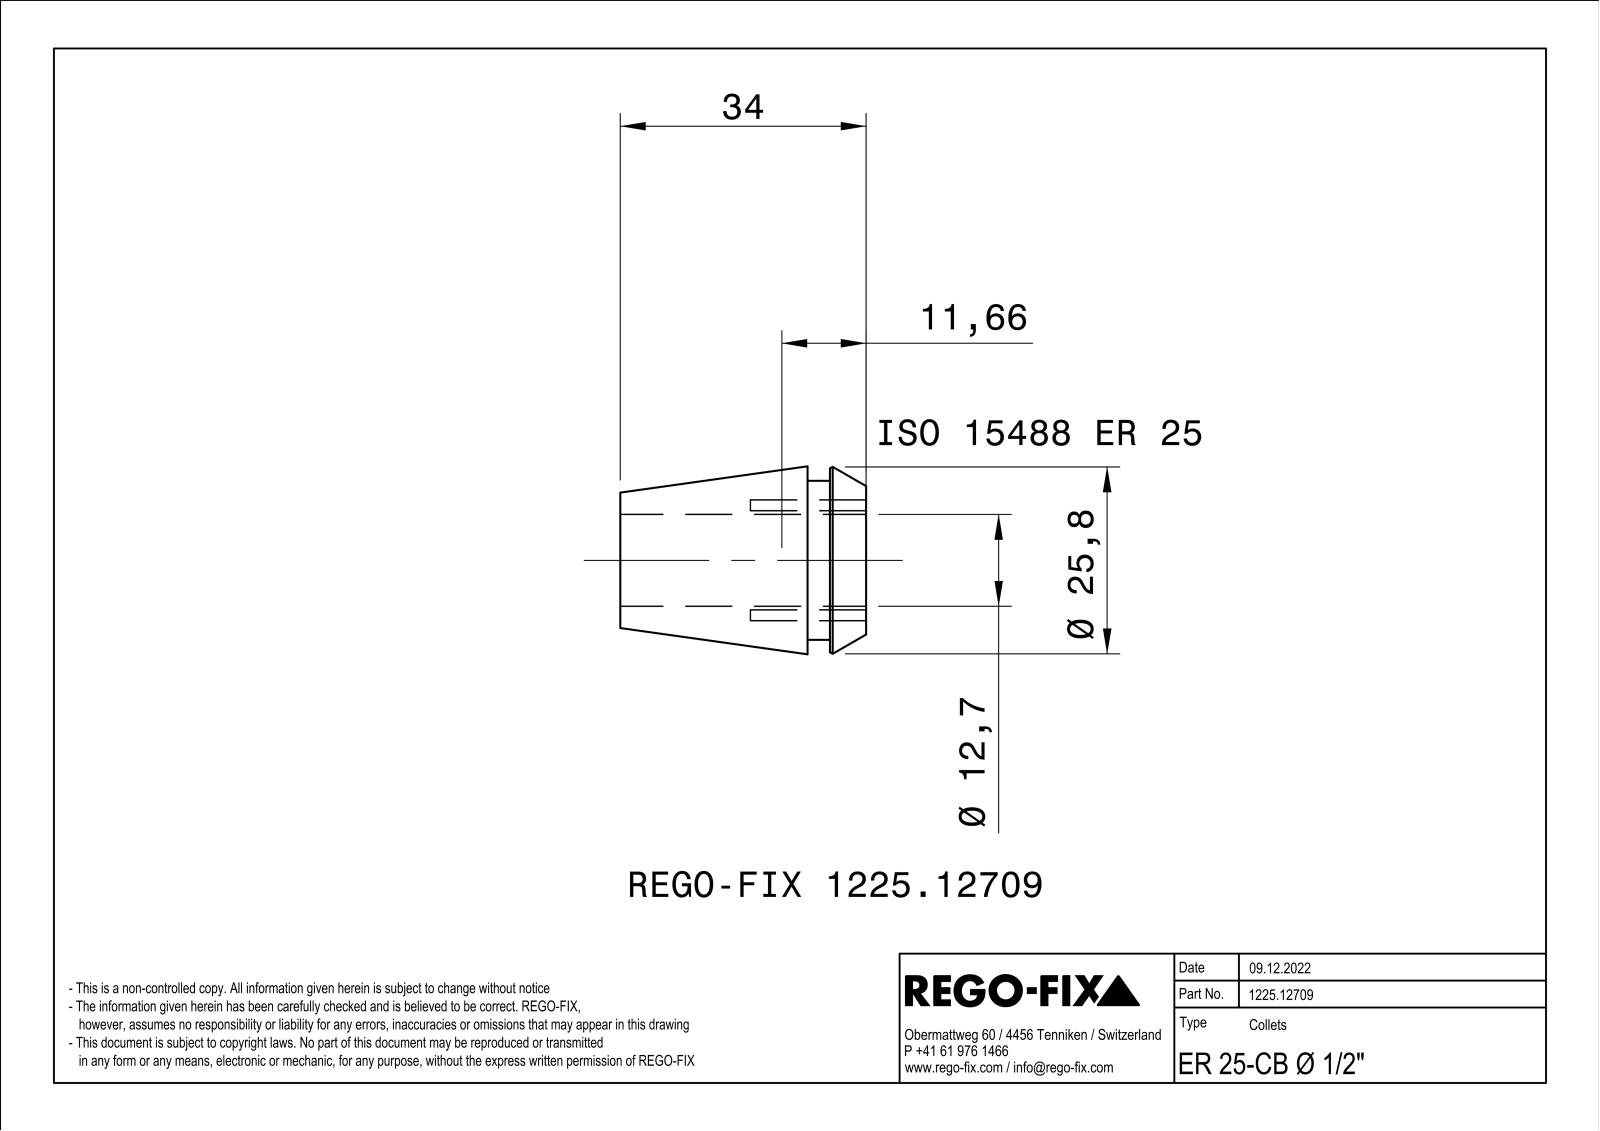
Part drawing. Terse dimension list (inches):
name: NOCUT
written by: SIEMENS PLM Software Solid Edge ST10 (AUTOMOTIVE_DESIGN)
unit: in
bodies: 1 solid, 178 faces (64 planar, 21 cylindrical, 93 other)
size: 1.339 × 1.023 × 1.023
volume: 0.469 in³; area: 12.12 in²
holes: 4× ⌀0.059, 1× ⌀0.5
bosses: 1× ⌀1.024, 1× ⌀0.866
face distances: 0.031, 0.197, 1.339, 1.142, 0.319, 0.122, 1.02
hole spacings: 0.299, 0.423, 0.598
